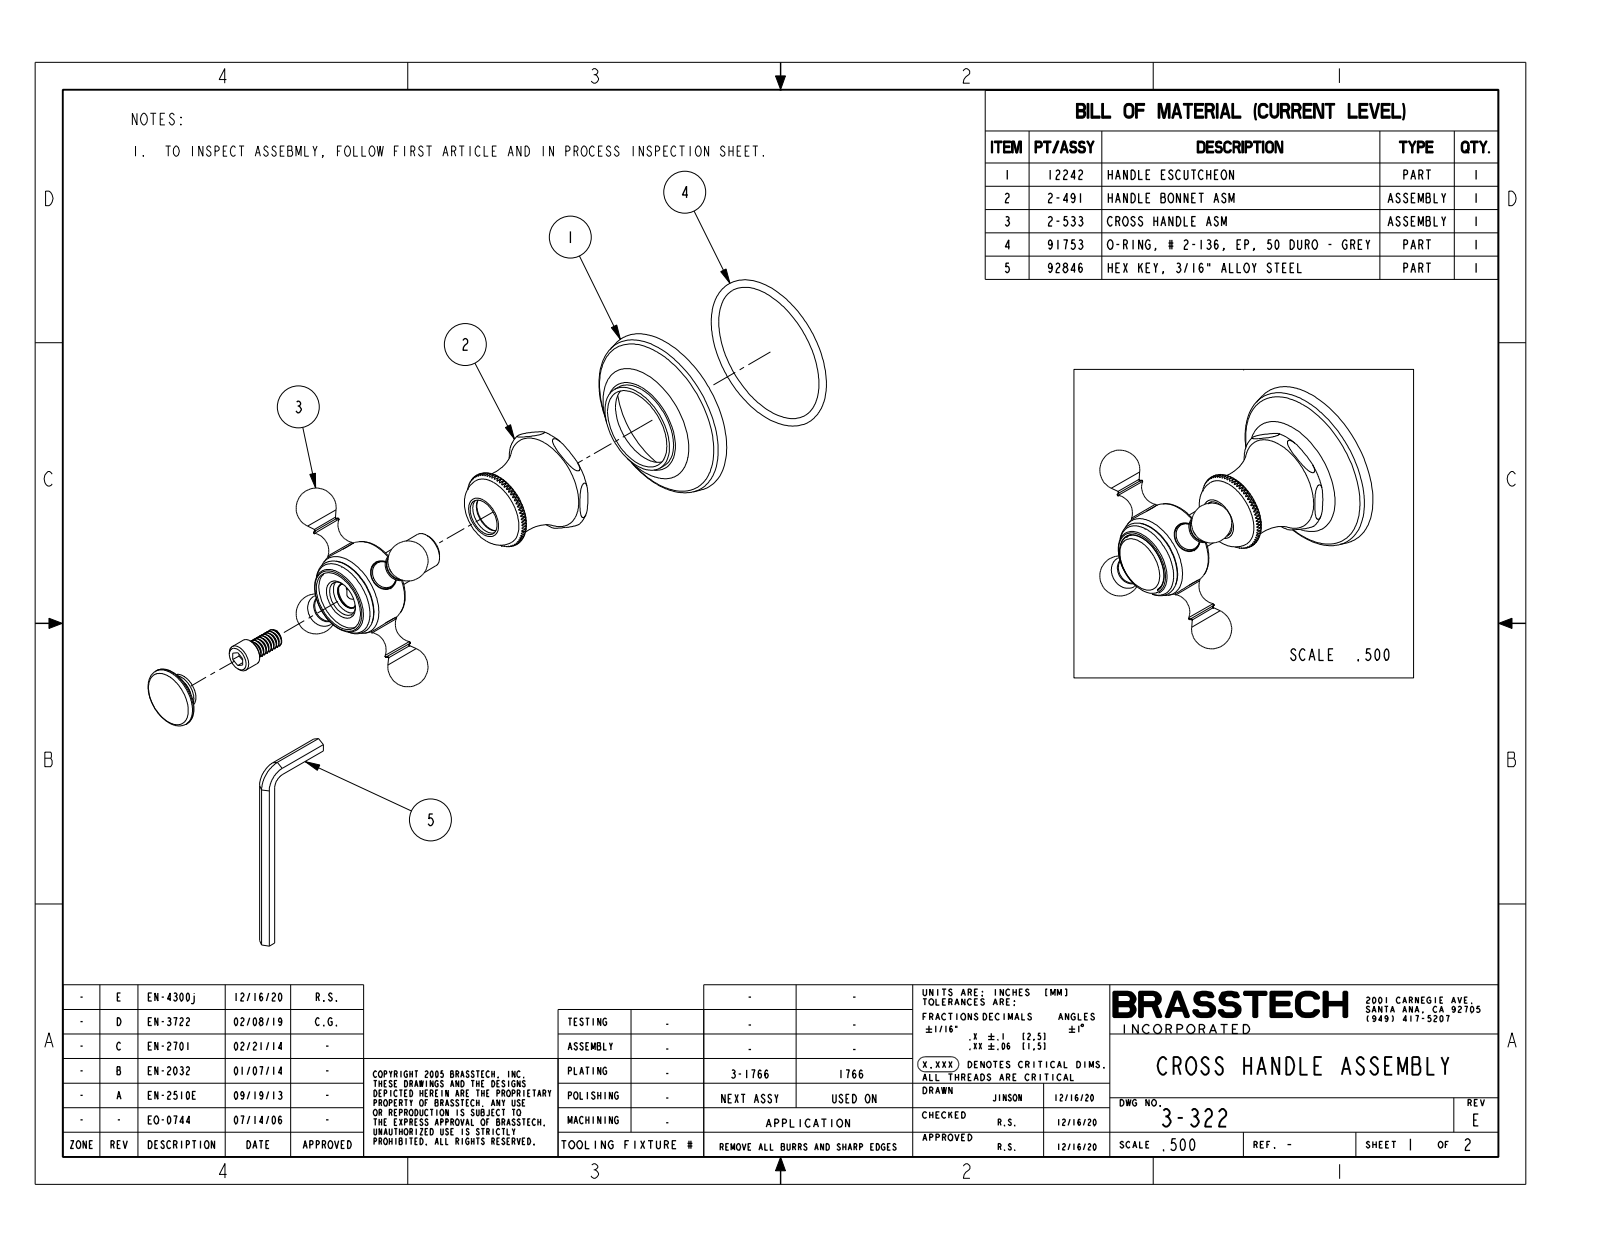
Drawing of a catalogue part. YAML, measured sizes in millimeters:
part_name: "30348"
step_written_by: "CREO PARAMETRIC BY PTC INC, 2018400 (CONFIG_CONTROL_DESIGN)"
units: millimeters
bodies: {solids: 1, faces: 268, planar: 160, cylindrical: 22, other: 86}
overall_size: [86.6, 78, 78]
volume: 67760
surface_area: 16460
round_holes:
  - {diameter: 10.4, count: 2}
  - {diameter: 21.7, count: 1}
round_bosses_or_shafts:
  - {diameter: 10, count: 2}
  - {diameter: 21.3, count: 1}
  - {diameter: 12.7, count: 1}
face_to_face_distances: [64.5, 34.9, 82.6, 18, 19.1, 83.8, 19.3, 1.3, 35, 46.1]
